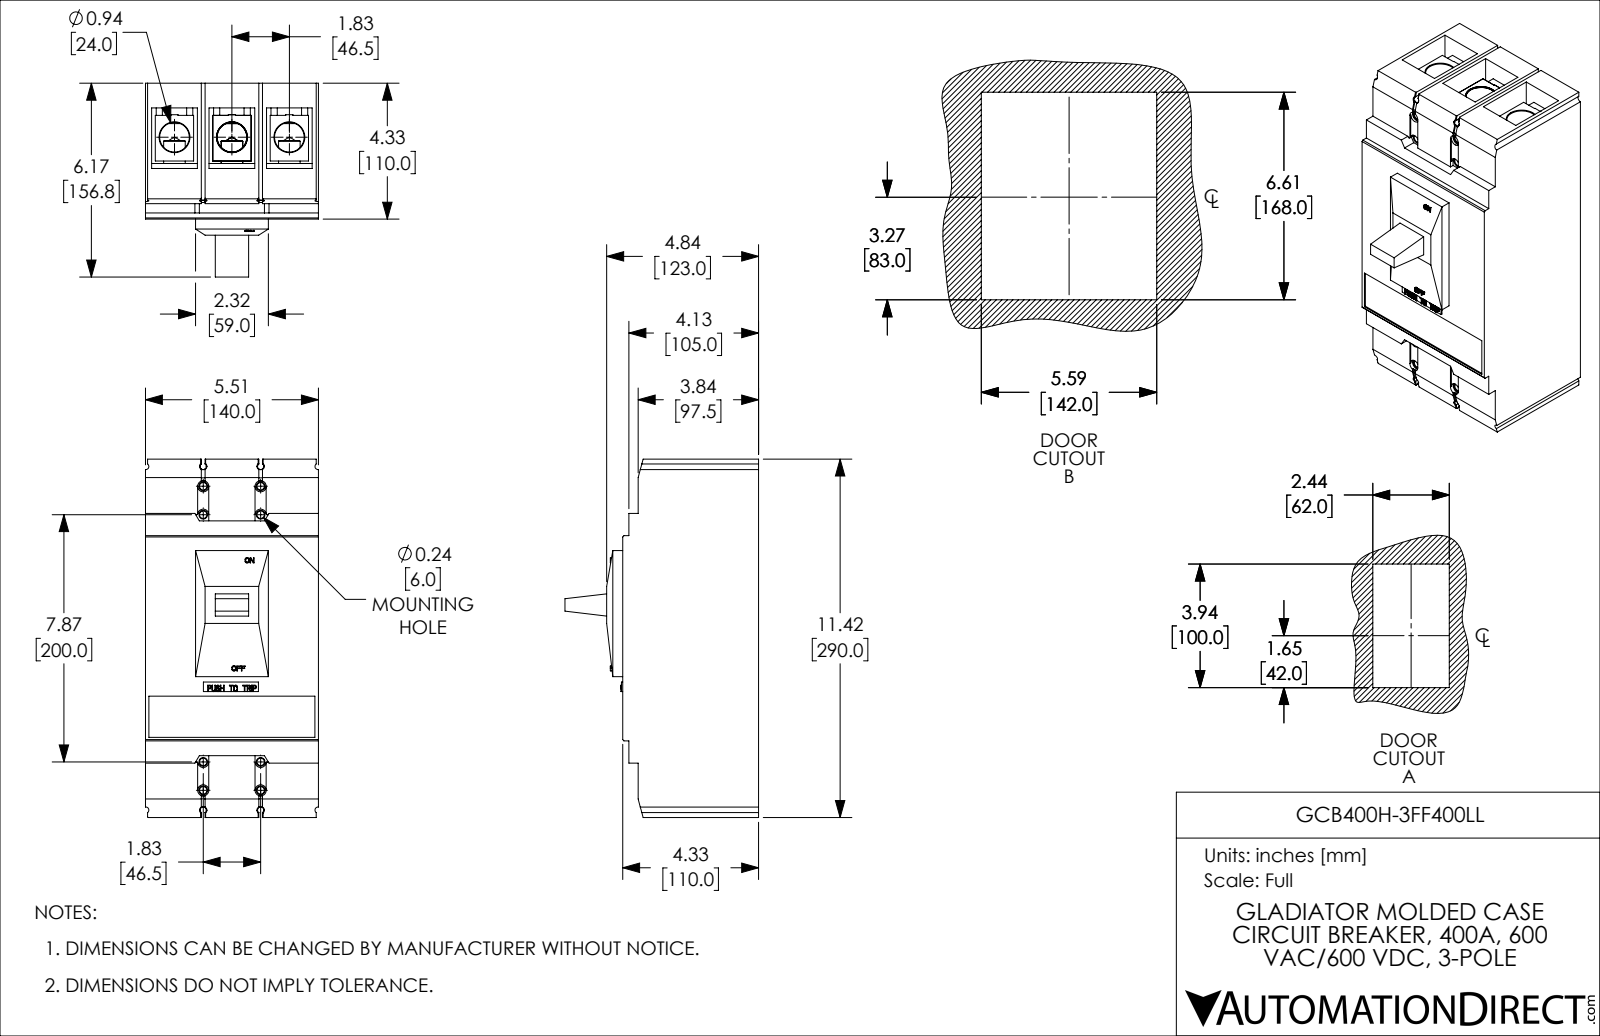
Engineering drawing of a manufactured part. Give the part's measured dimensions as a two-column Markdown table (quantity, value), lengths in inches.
| quantity | value |
| --- | --- |
| part name | GCB400H-3FF400LL |
| STEP written by | SolidWorks 2021 (CONFIG_CONTROL_DESIGN) |
| units | inches |
| bodies | 26 solids, 1319 faces (935 planar, 200 cylindrical, 184 other) |
| overall size | 11.417 × 6.173 × 5.512 |
| volume | 245.8 in³ |
| surface area | 525.8 in² |
| round holes (diameter × count) | 0.236 × 8, 0.413 × 6, 0.594 × 6, 0.688 × 6, 0.197 × 4, 0.354 × 4, 0.945 × 3 |
| round bosses / shafts (diameter × count) | 0.575 × 6, 0.394 × 6, 0.75 × 1 |
| partial cylindrical surfaces (radius × count) | 0.098 × 28, 0.039 × 8, 0.177 × 4 |
| main face-to-face distances | 1.831, 5.512, 0.492, 1.457, 0.118, 1.339, 1.772, 1.713, 1.949, 0.197 |
| hole center spacings | 1.831, 0.968, 1.089, 1.316, 8.514, 9.415, 10.042, 0.63 |
